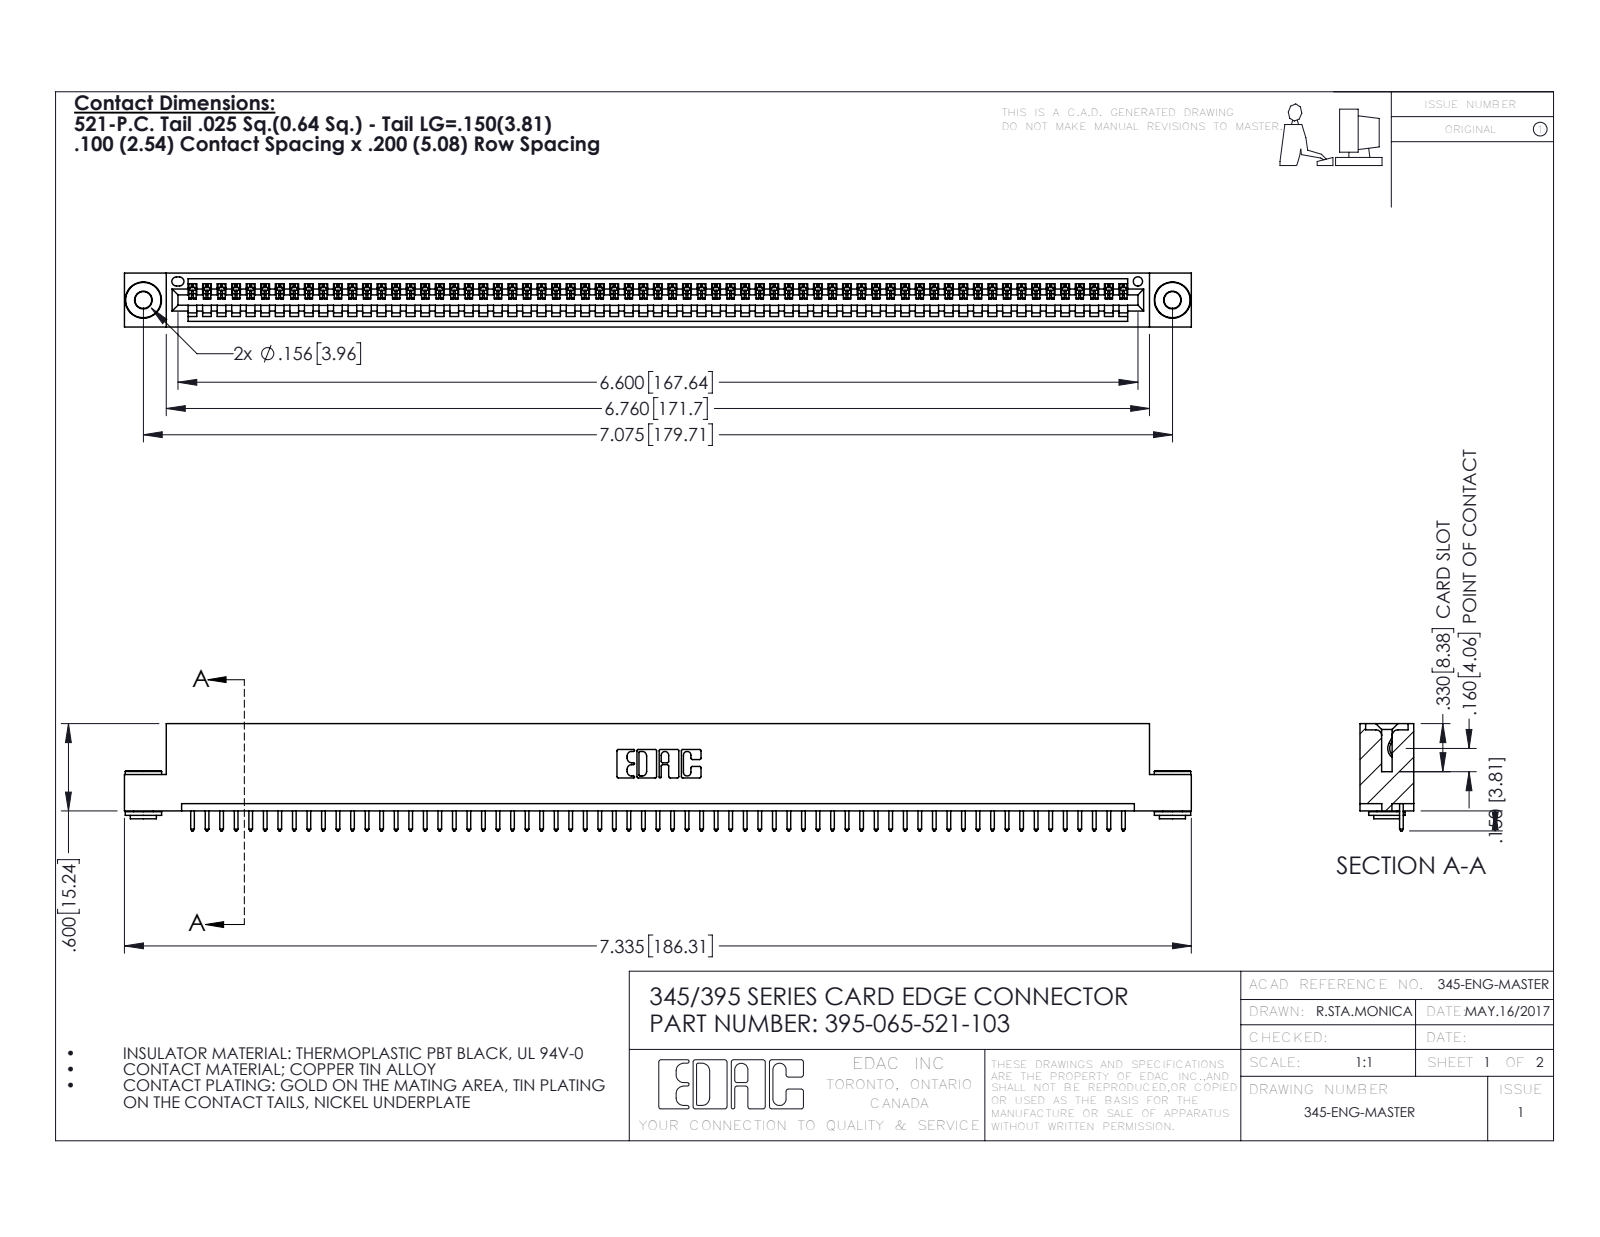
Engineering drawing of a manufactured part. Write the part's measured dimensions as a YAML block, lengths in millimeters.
part_name: "345-292-001_345-293-121; 395-065-521-103; 345-250-002_345-250-002-102; 345 Part_Flush Mounting Lugs - 0.156 Dia-TH"
step_written_by: "SolidWorks 2016 (CONFIG_CONTROL_DESIGN)"
units: millimeters
bodies: {solids: 68, faces: 3934, planar: 2690, cylindrical: 1236, other: 8}
overall_size: [186.3, 18.7, 9.4]
volume: 17710
surface_area: 23350
round_holes:
  - {diameter: 2.9, count: 2}
  - {diameter: 4, count: 2}
  - {diameter: 1.6, count: 1}
round_bosses_or_shafts:
  - {diameter: 6.4, count: 2}
  - {diameter: 4.6, count: 2}
  - {diameter: 3.5, count: 2}
partial_cylinders:
  - {radius: 0.2, count: 130}
  - {radius: 0.3, count: 130}
  - {radius: 0.3, count: 22}
  - {radius: 0.2, count: 6}
  - {radius: 0.8, count: 6}
  - {radius: 0.7, count: 3}
  - {radius: 0.8, count: 2}
  - {radius: 1, count: 2}
face_to_face_distances: [1.8, 7.6, 9.4, 5.1, 0.6, 2.5, 6.9, 5.7, 3.8, 1.8]
hole_center_spacings: [6.9, 173.7, 179.7]
